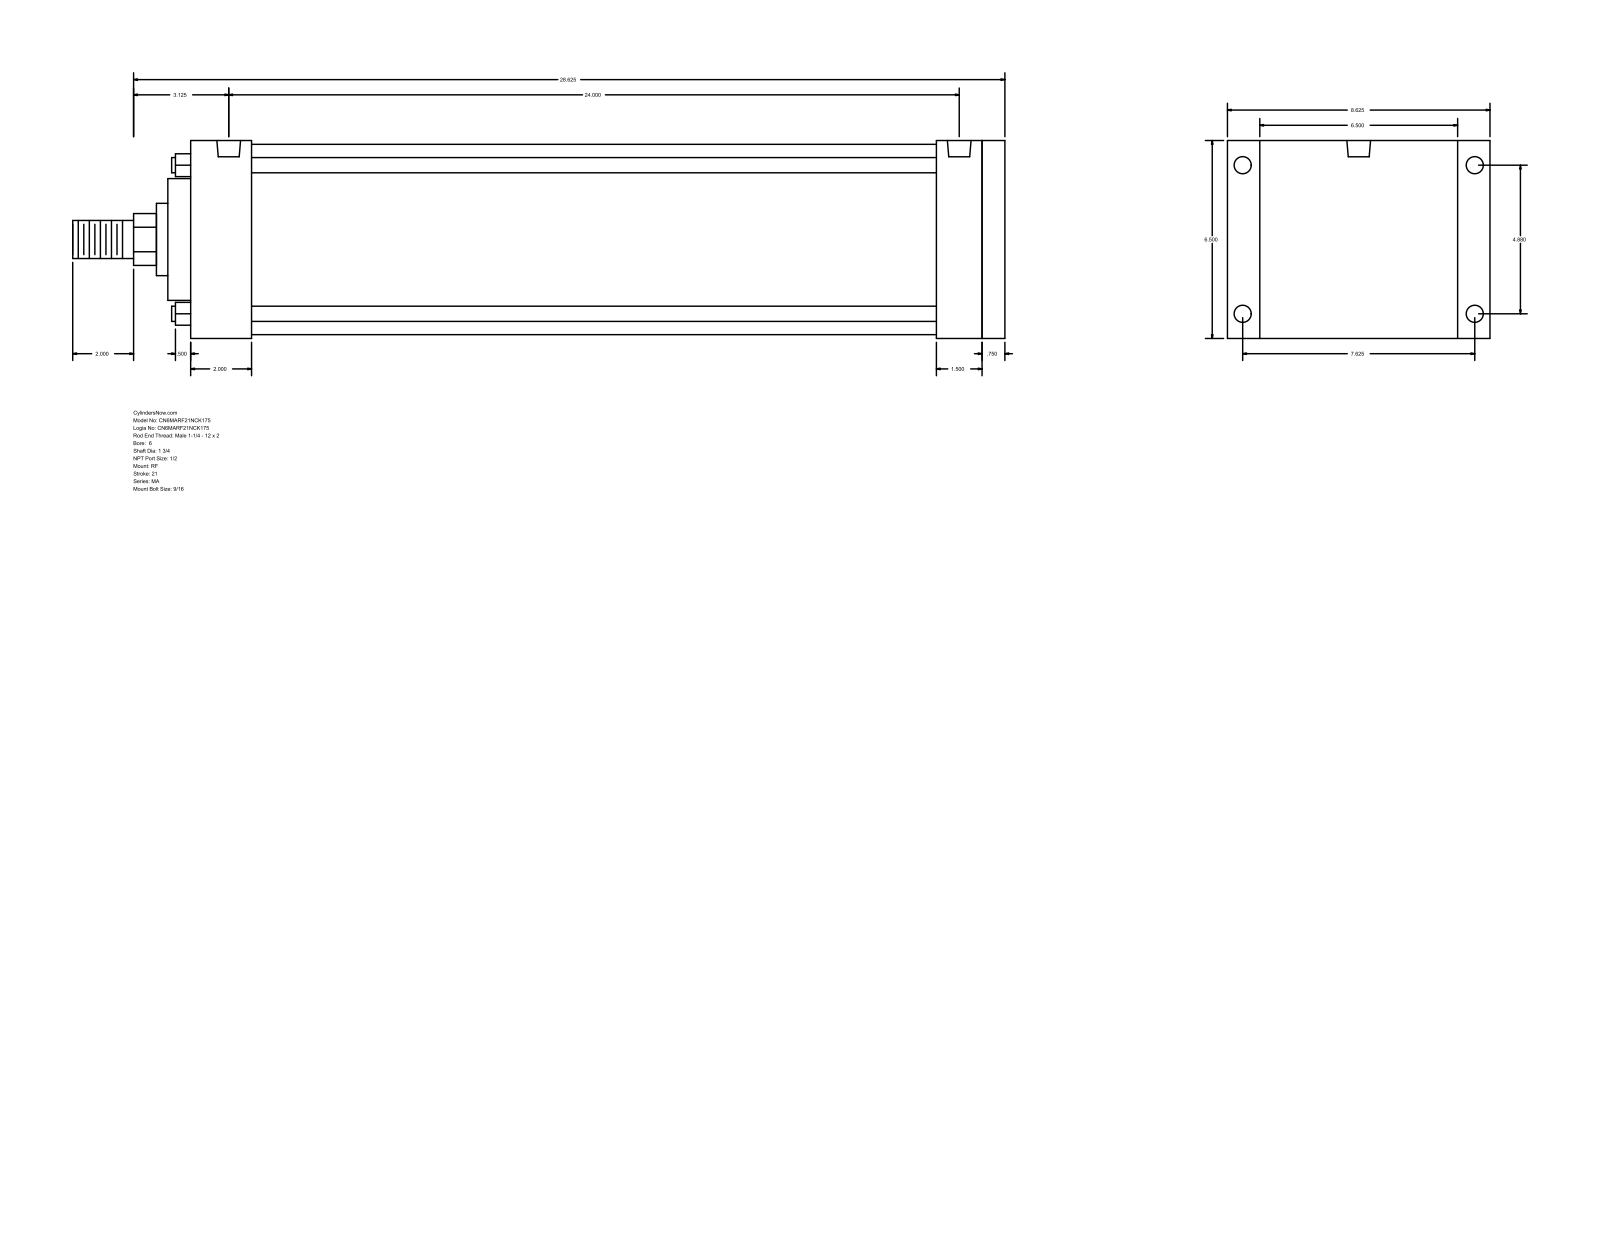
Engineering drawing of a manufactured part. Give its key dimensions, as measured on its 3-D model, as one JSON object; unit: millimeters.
{"part_name": "MA_RF__0600_1.75", "step_written_by": "GSSL Pune (CONFIG_CONTROL_DESIGN)", "units": "millimeters", "bodies": {"solids": 0, "faces": 94, "planar": 65, "cylindrical": 29, "other": 0}, "overall_size": [777.88, 219.07, 165.1], "round_holes": [[14.29, 4], [17.46, 4], [19.77, 2]], "round_bosses_or_shafts": [[12.7, 4], [158.75, 1], [101.6, 1], [60.33, 1], [44.45, 1], [31.75, 1]], "partial_cylinders_radius": [[21.63, 1]], "face_to_face_distances": [165.1, 679.46, 660.4, 19.06, 38.1, 50.8, 19.05, 609.6, 628.66, 622.3], "hole_center_spacings": [123.96, 193.68, 229.95, 609.6]}
